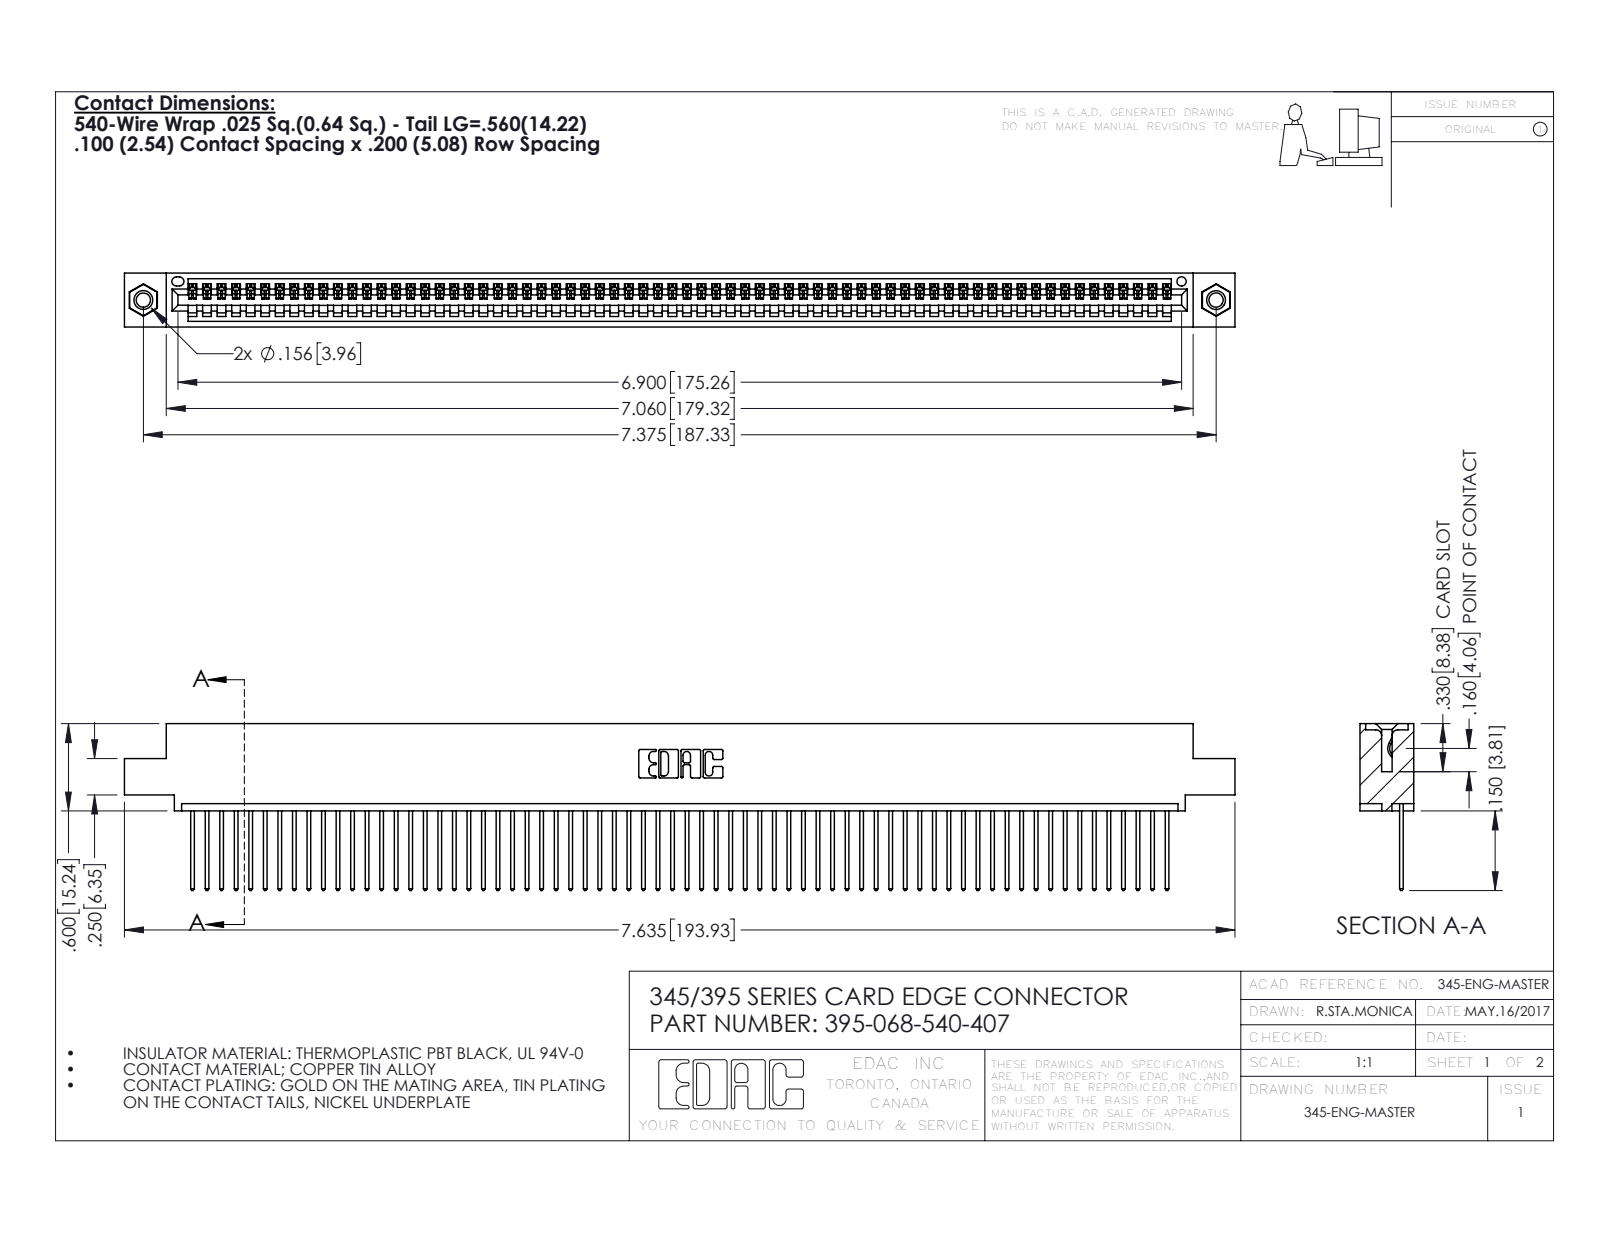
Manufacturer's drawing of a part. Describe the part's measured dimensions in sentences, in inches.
The part is named "345-292-001_345-293-140; 395-068-540-407; 345-250-001_345-250-005-103; 345 Part_0.110 Offset - 0.156 Dia-TI". Its 3-D file was written by "SolidWorks 2016 (CONFIG_CONTROL_DESIGN)". It is 71 solids with 4134 faces: 2836 planar, 1282 cylindrical and 16 other. Overall it measures 7.635 by 1.147 by 0.37 inches. Its volume is 1.137 cubic inches and its surface area 40.14 square inches. Round holes: 2 of diameter 0.098, 2 of diameter 0.125, 2 of diameter 0.156, 1 of diameter 0.064. Round bosses or shafts: 2 of diameter 0.155. Partial cylindrical surfaces (rounded edges, fillets, slot ends): 136 of radius 0.006, 136 of radius 0.01, 22 of radius 0.01, 6 of radius 0.007, 6 of radius 0.031, 3 of radius 0.026, 2 of radius 0.031, 2 of radius 0.04. The main face-to-face distances are 0.072, 0.298, 0.37, 0.098, 0.272, 0.025, 0.2, 0.225, 0.149, 0.072. The hole center spacings are 0.27, 7.139, 7.375.
